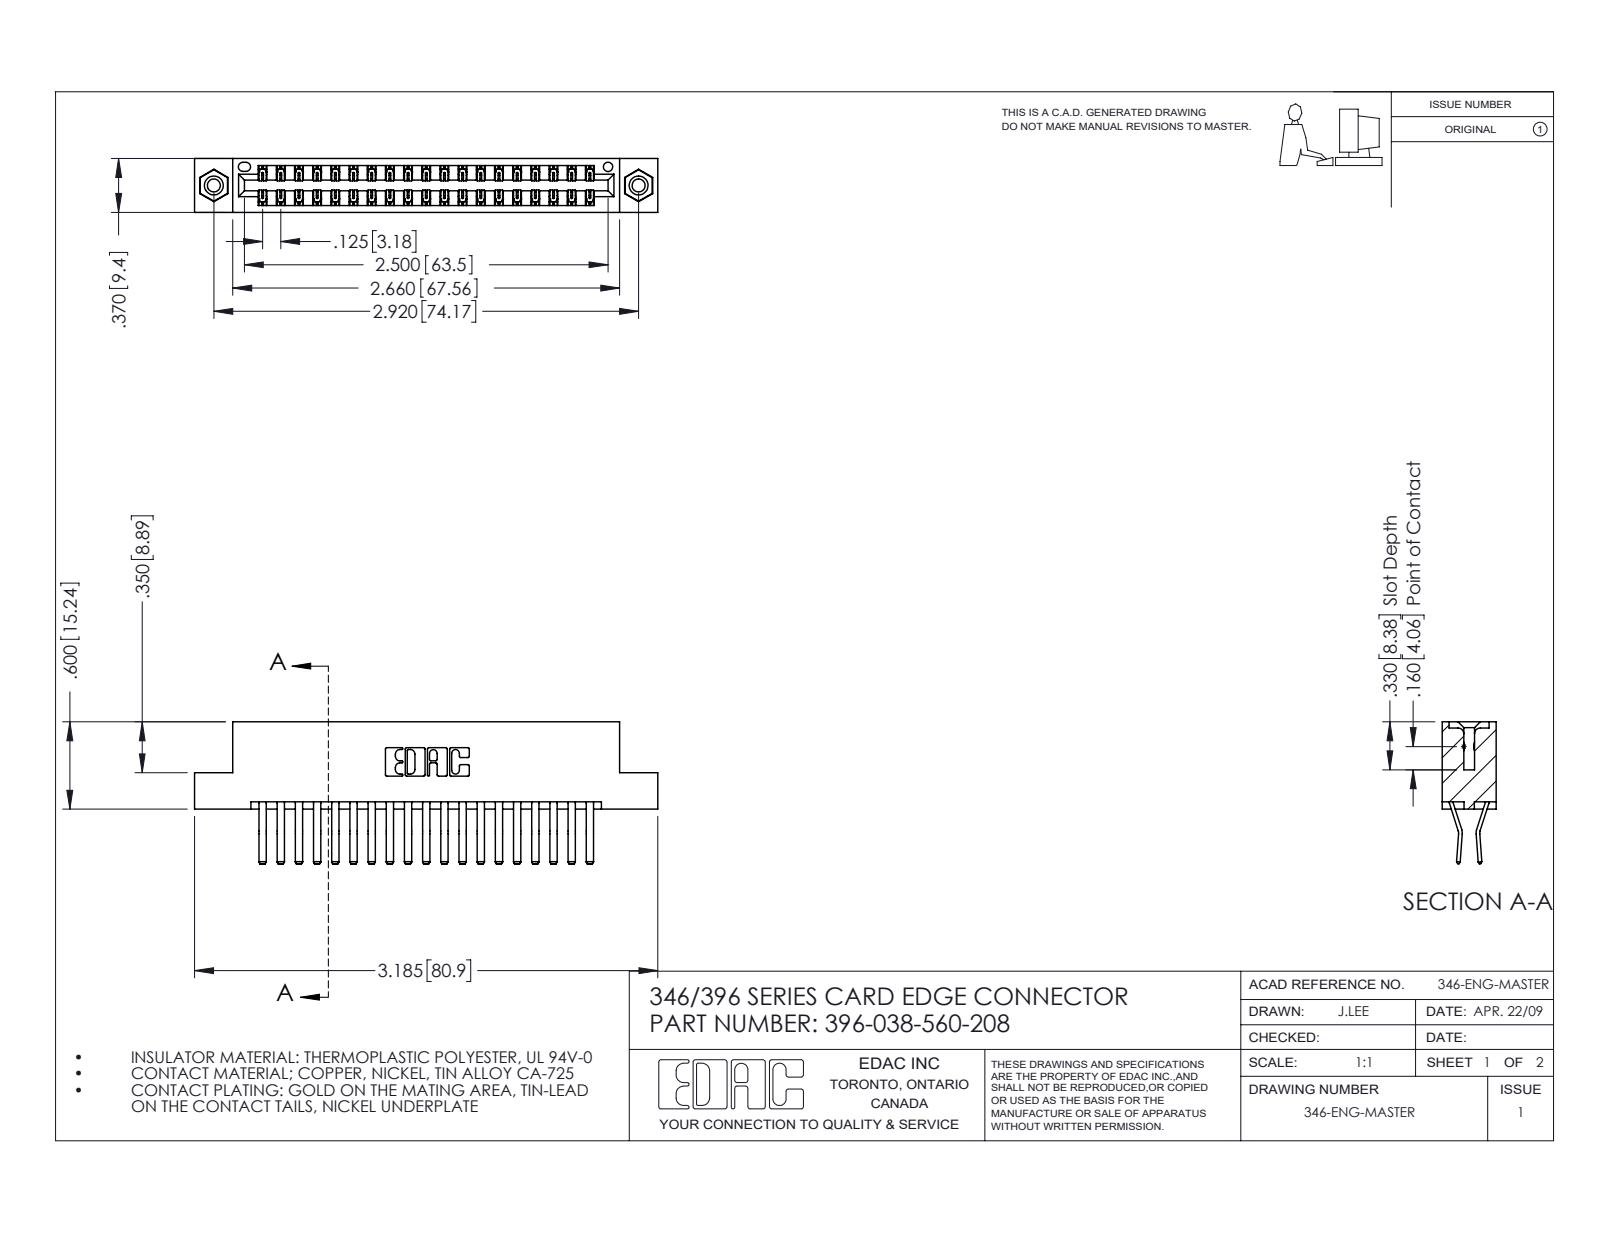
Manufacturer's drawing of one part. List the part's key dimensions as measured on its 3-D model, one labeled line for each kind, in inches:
Part name (STEP PRODUCT): 345-292-001_560 Tail; 346 Part_Flush Mounting Lugs - 0.156 Dia-TI; 396-038-560-208; 345-250-001_345-250-003-102
STEP written by: SolidWorks 2016 (CONFIG_CONTROL_DESIGN)
Units: inches
Bodies: 41 solids, 2234 faces (1438 planar, 780 cylindrical, 16 other)
Overall size (bounding box): 3.185 × 0.975 × 0.37
Volume: 0.485 in³ · Surface area: 17.44 in²
Round holes (diameter × count): ⌀0.089 ×2, ⌀0.125 ×2, ⌀0.156 ×2, ⌀0.064 ×1
Round bosses / shafts (diameter × count): ⌀0.155 ×2
Partial cylindrical surfaces — rounded edges, fillets, slot ends (radius × count): R0.006 ×57, R0.01 ×22, R0.007 ×6, R0.031 ×6, R0.026 ×3, R0.01 ×2, R0.014 ×2, R0.022 ×2
Main face-to-face distances: 0.048, 0.322, 0.25, 0.37, 0.025, 0.072, 0.298, 0.275, 0.148, 0.222
Hole centre spacings: 0.246, 2.713, 2.92
